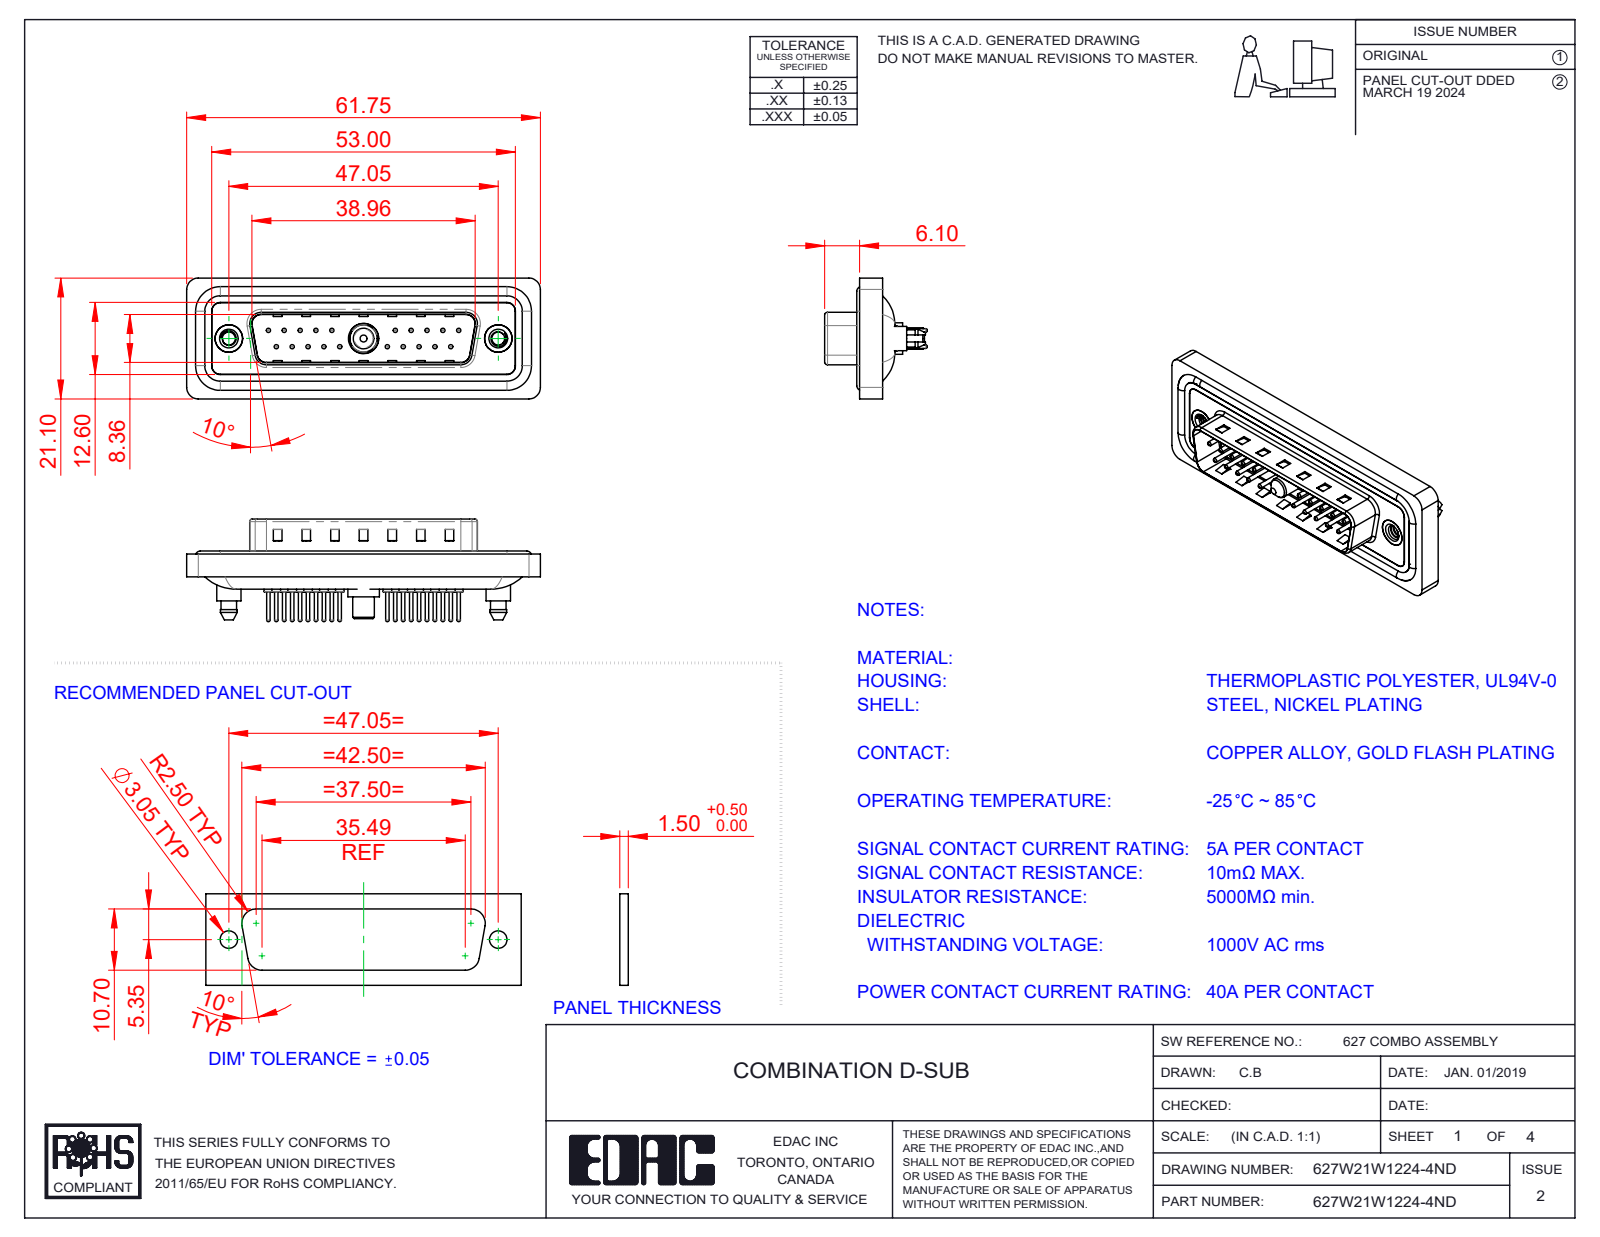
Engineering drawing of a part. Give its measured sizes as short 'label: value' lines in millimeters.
name: 627W21W1224-4ND; 627Combo Threaded Boardlock_5; 627Combo Contact Row 1_24; 627Combo Shell Rear_25 Contacts (+6 more)
written by: SolidWorks 2023 (CONFIG_CONTROL_DESIGN)
unit: mm
bodies: 29 solids, 1320 faces (375 planar, 527 cylindrical, 418 other)
size: 61.75 × 21.1 × 17.9
volume: 7 351 mm³; area: 12 300 mm²
holes: 20× ⌀0.75, 20× ⌀1.6, 20× ⌀2, 2× ⌀2.26, 2× ⌀4, 2× ⌀4.8, 2× ⌀5, 1× ⌀4.85, 1× ⌀5.3
bosses: 20× ⌀1.5, 20× ⌀0.6, 4× ⌀1.6, 2× ⌀5.4, 2× ⌀4.9, 2× ⌀4.25, 1× ⌀5.5, 1× ⌀5.2
rounds: 24× R1.5, 18× R2, 10× R1.6, 8× R0.5, 4× R0.25, 4× R0.6, 4× R0.65, 4× R0.9
face distances: 0.4, 1.5, 1.1, 1.6, 3.1, 0.5, 2.9, 4.1, 0.82, 9.58
hole spacings: 3.16, 2.77, 5.54, 8.31, 5.04, 19.39, 20.97, 22.16
